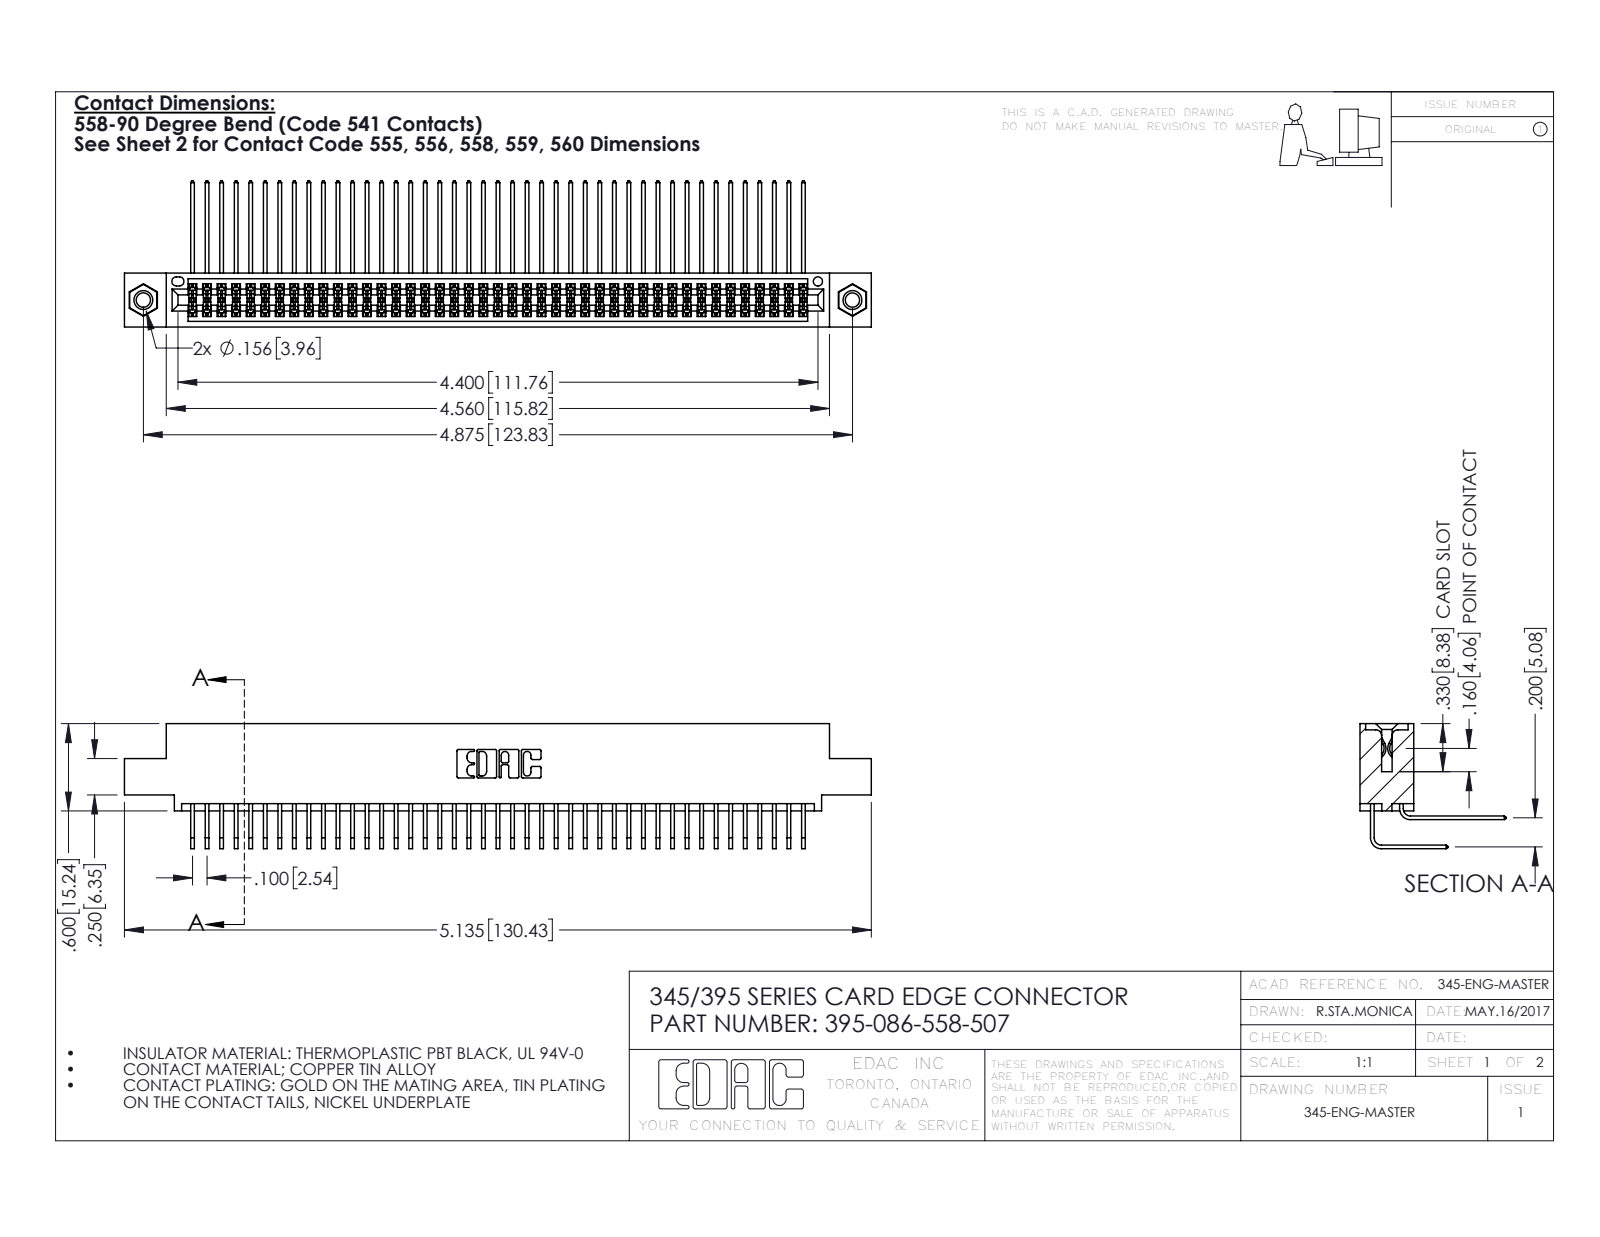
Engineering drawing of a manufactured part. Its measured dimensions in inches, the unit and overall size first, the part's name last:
Units: inches
Overall size (bounding box): 5.135 × 1.005 × 0.859
Round holes (diameter × count): ⌀0.098 ×2, ⌀0.125 ×2, ⌀0.156 ×2, ⌀0.064 ×1
Round bosses / shafts (diameter × count): ⌀0.155 ×2
Partial cylindrical surfaces — rounded edges, fillets, slot ends (radius × count): R0.006 ×130, R0.01 ×22, R0.007 ×6, R0.031 ×6, R0.026 ×3, R0.014 ×2, R0.019 ×2, R0.022 ×2
Main face-to-face distances: 0.072, 0.298, 0.2, 0.37, 0.098, 0.272, 0.025, 0.225, 0.025, 0.175
Hole centre spacings: 0.27, 4.639, 4.875
Volume: 0.799 in³ · Surface area: 33.82 in²
Bodies: 89 solids, 4662 faces (3126 planar, 1520 cylindrical, 16 other)
Part name (STEP PRODUCT): 345-250-001_345-250-005-103; 345-292-001_558 Tail - 2; 395-086-558-507; 345-292-001_558 559 Tail - 1 (+1 more)
STEP written by: SolidWorks 2016 (CONFIG_CONTROL_DESIGN)
